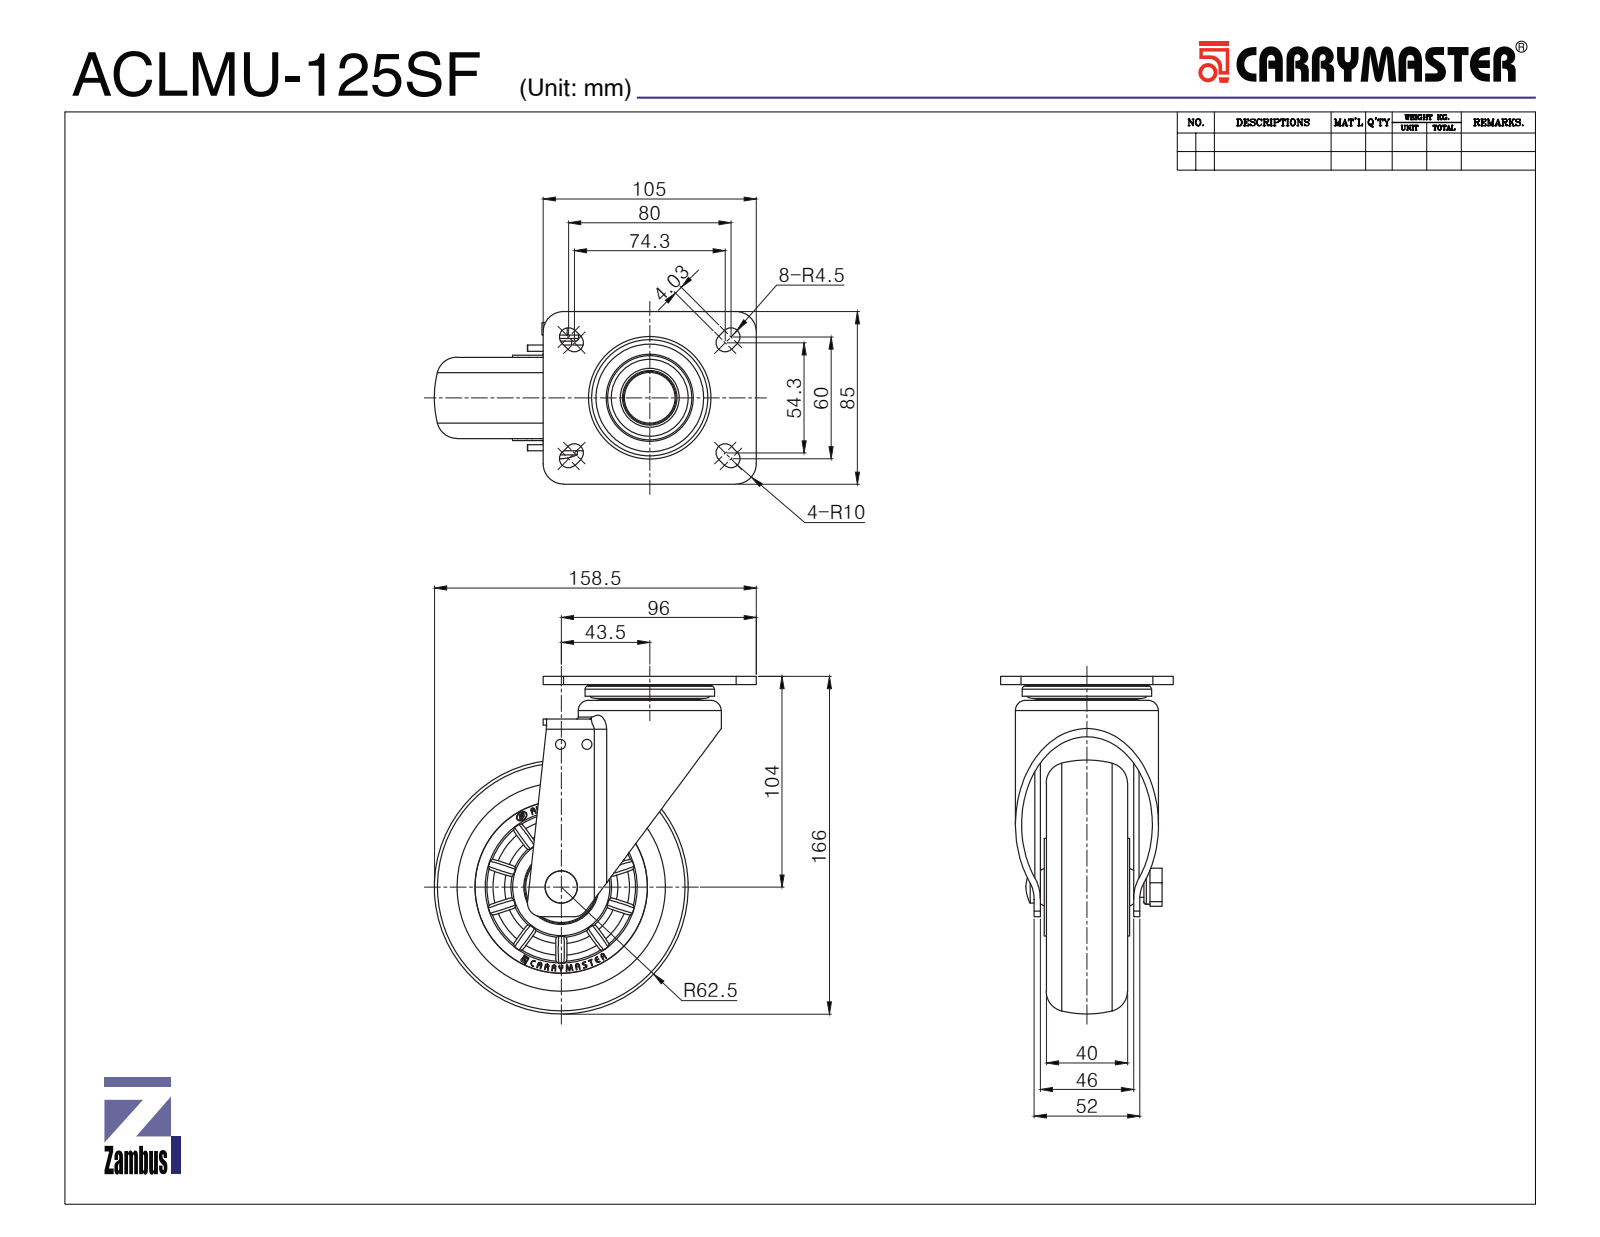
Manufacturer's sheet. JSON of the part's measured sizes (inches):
{"part_name": "ACLMU-125SF", "step_written_by": "SolidWorks 2015 (CONFIG_CONTROL_DESIGN)", "units": "inches", "bodies": {"solids": 13, "faces": 1595, "planar": 891, "cylindrical": 230, "other": 474}, "overall_size": [6.547, 6.244, 3.346], "volume_in3": 33.26, "surface_area_in2": 275.7, "round_holes": [[0.067, 2], [0.197, 2], [0.335, 1], [0.394, 1], [0.472, 1], [0.575, 1], [1.181, 1], [1.26, 1], [1.263, 1], [1.768, 1], [2.008, 1], [2.374, 1]], "round_bosses_or_shafts": [[0.026, 2], [4.134, 1], [2.772, 1], [2.508, 1], [2.382, 1], [2.256, 1], [1.378, 1], [0.762, 1]], "partial_cylinders_radius": [[0.039, 40], [0.472, 20], [0.177, 8], [0.059, 4], [0.394, 4], [0.025, 2], [0.033, 2], [0.046, 2]], "face_to_face_distances": [0.118, 0.157, 0.236, 1.811, 1.693, 1.929, 1.575, 0.197, 1.614, 0.315], "hole_center_spacings": [0.512, 1.496, 1.606, 1.606, 2.768, 2.812, 4.196, 4.252]}
